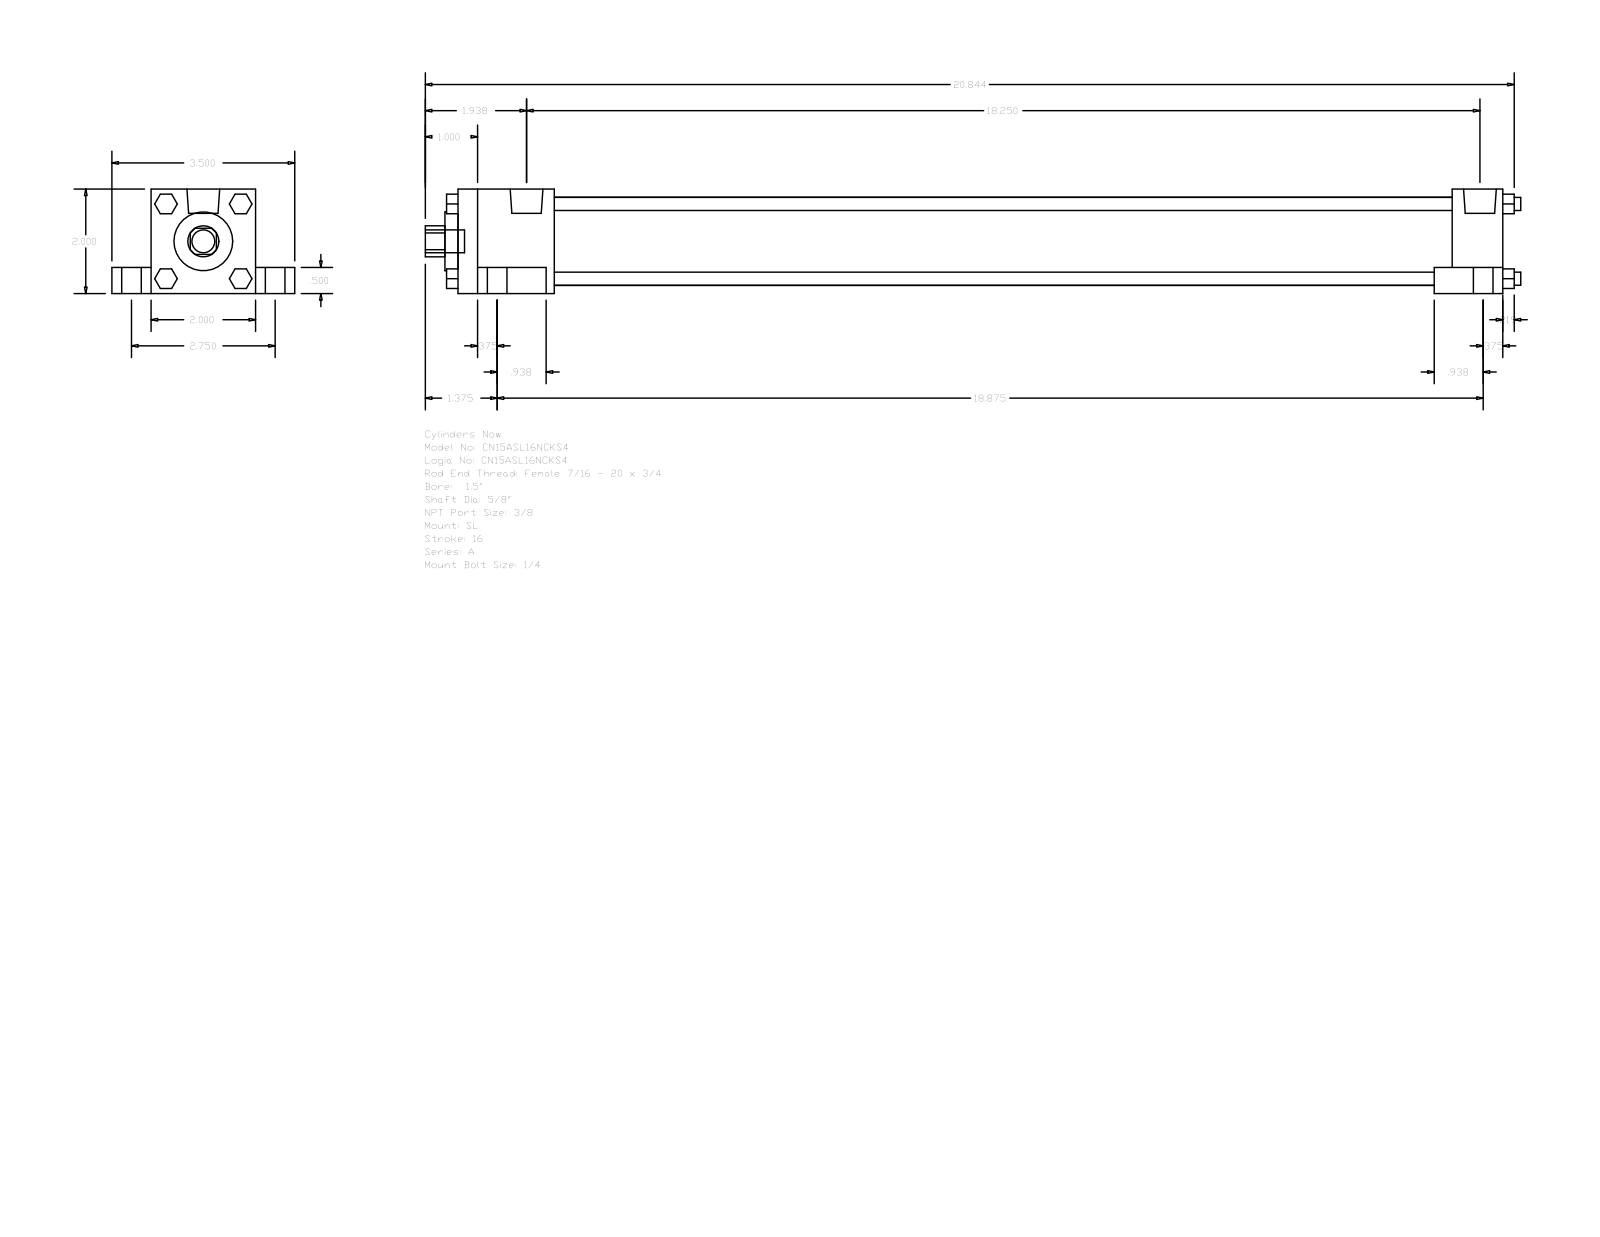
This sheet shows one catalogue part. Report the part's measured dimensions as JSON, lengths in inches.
{"part_name": "A_SL__0150_0.625", "step_written_by": "GSSL Pune (CONFIG_CONTROL_DESIGN)", "units": "inches", "bodies": {"solids": 0, "faces": 148, "planar": 112, "cylindrical": 36, "other": 0}, "overall_size": [20.969, 3.5, 2], "round_holes": [[0.625, 1], [1.125, 1], [1.69, 1]], "round_bosses_or_shafts": [[0.625, 4], [0.375, 4], [0.25, 4], [0.219, 4], [0.627, 2], [0.437, 1]], "partial_cylinders_radius": [[0.297, 1]], "face_to_face_distances": [2, 0.75, 0.5, 1.5, 2.75, 20, 0.375, 1.313, 19.031, 0.969]}
